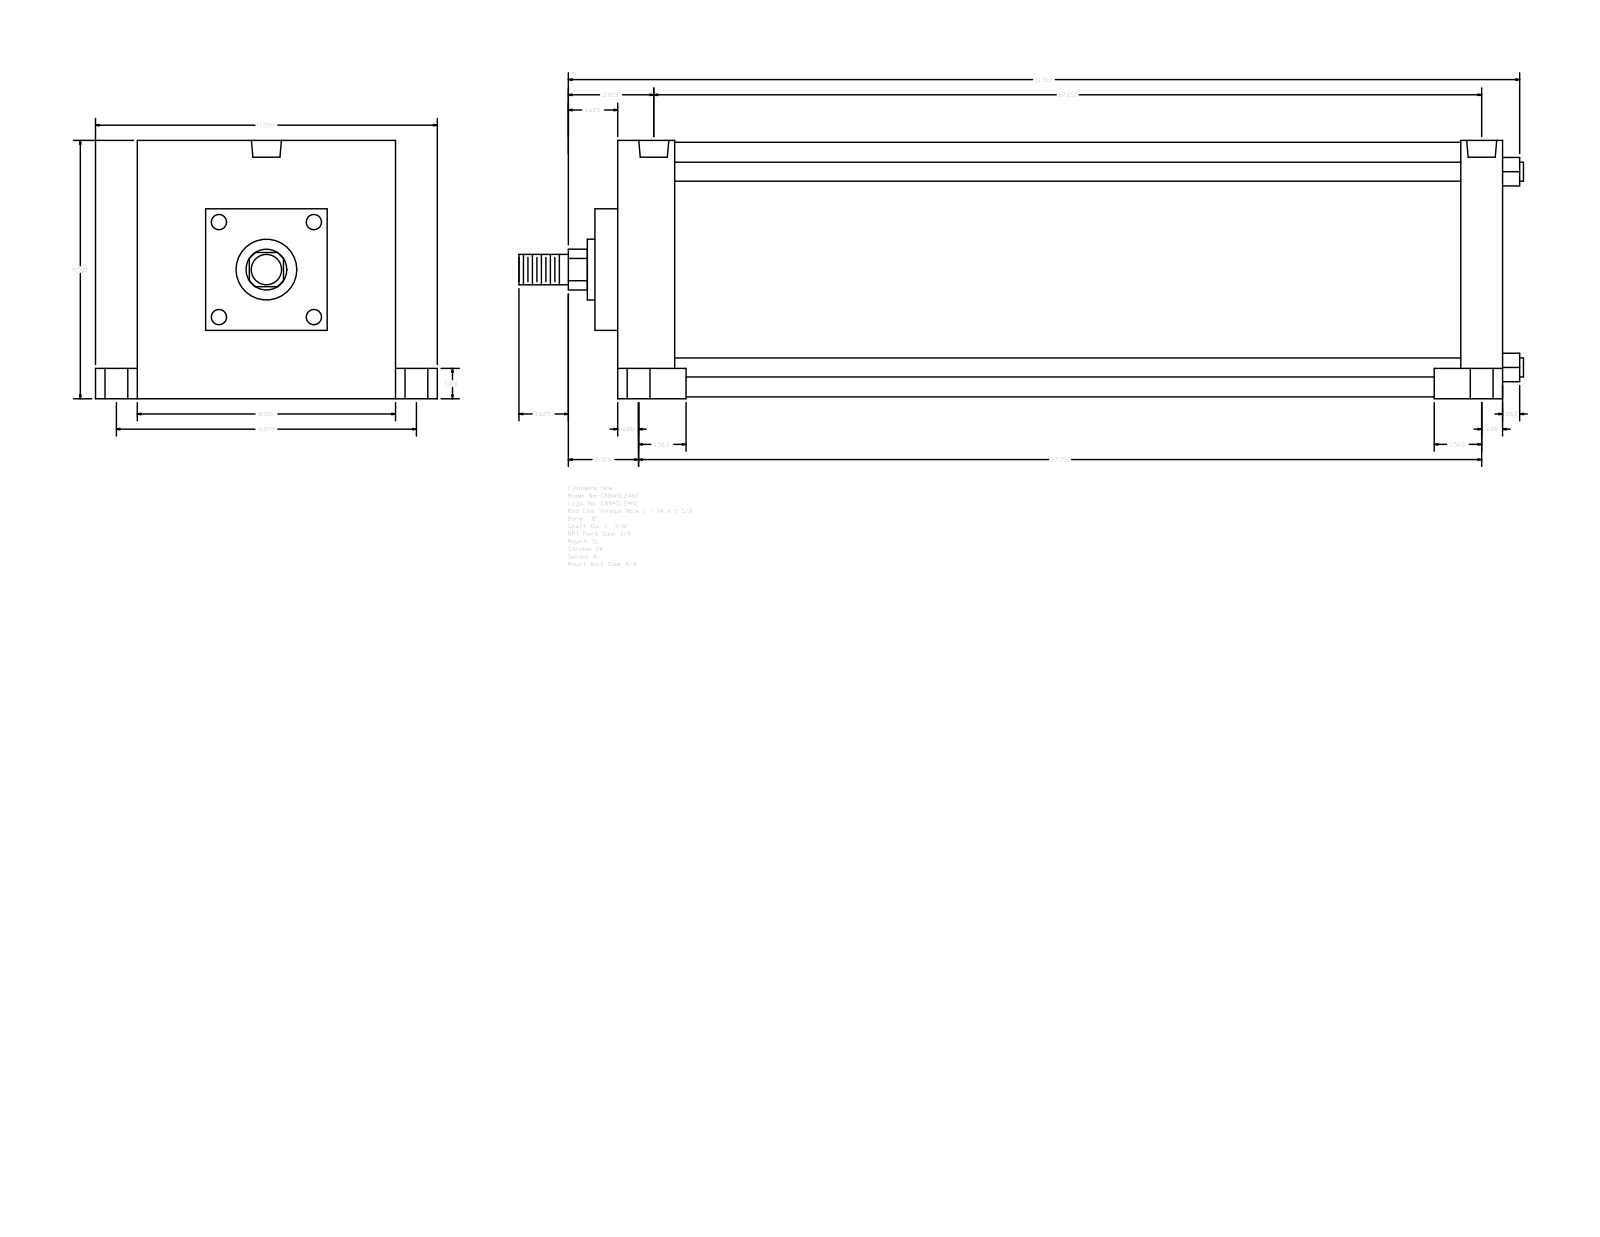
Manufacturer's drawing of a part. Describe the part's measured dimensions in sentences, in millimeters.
The part is named "A_SL__0800_1.375". Its 3-D file was written by "GSSL Pune (CONFIG_CONTROL_DESIGN)". It is 0 solids with 117 faces: 85 planar, 32 cylindrical and 0 other. Overall it measures 839.79 by 285.75 by 215.9 millimeters. Round holes: 4 of diameter 15.08, 4 of diameter 19.05, 4 of diameter 25.4, 2 of diameter 25.12. Round bosses or shafts: 4 of diameter 15.88, 1 of diameter 212.72, 1 of diameter 50.8, 1 of diameter 34.92, 1 of diameter 25.4. Partial cylindrical surfaces (rounded edges, fillets, slot ends): 1 of radius 17.06. The main face-to-face distances are 739.78, 215.9, 34.93, 57.15, 47.63, 692.15, 704.85, 657.22, 19.04, 66.67. The hole center spacings are 6.35, 125.41, 125.57, 126.05, 126.85, 250.82, 679.45, 685.8.
